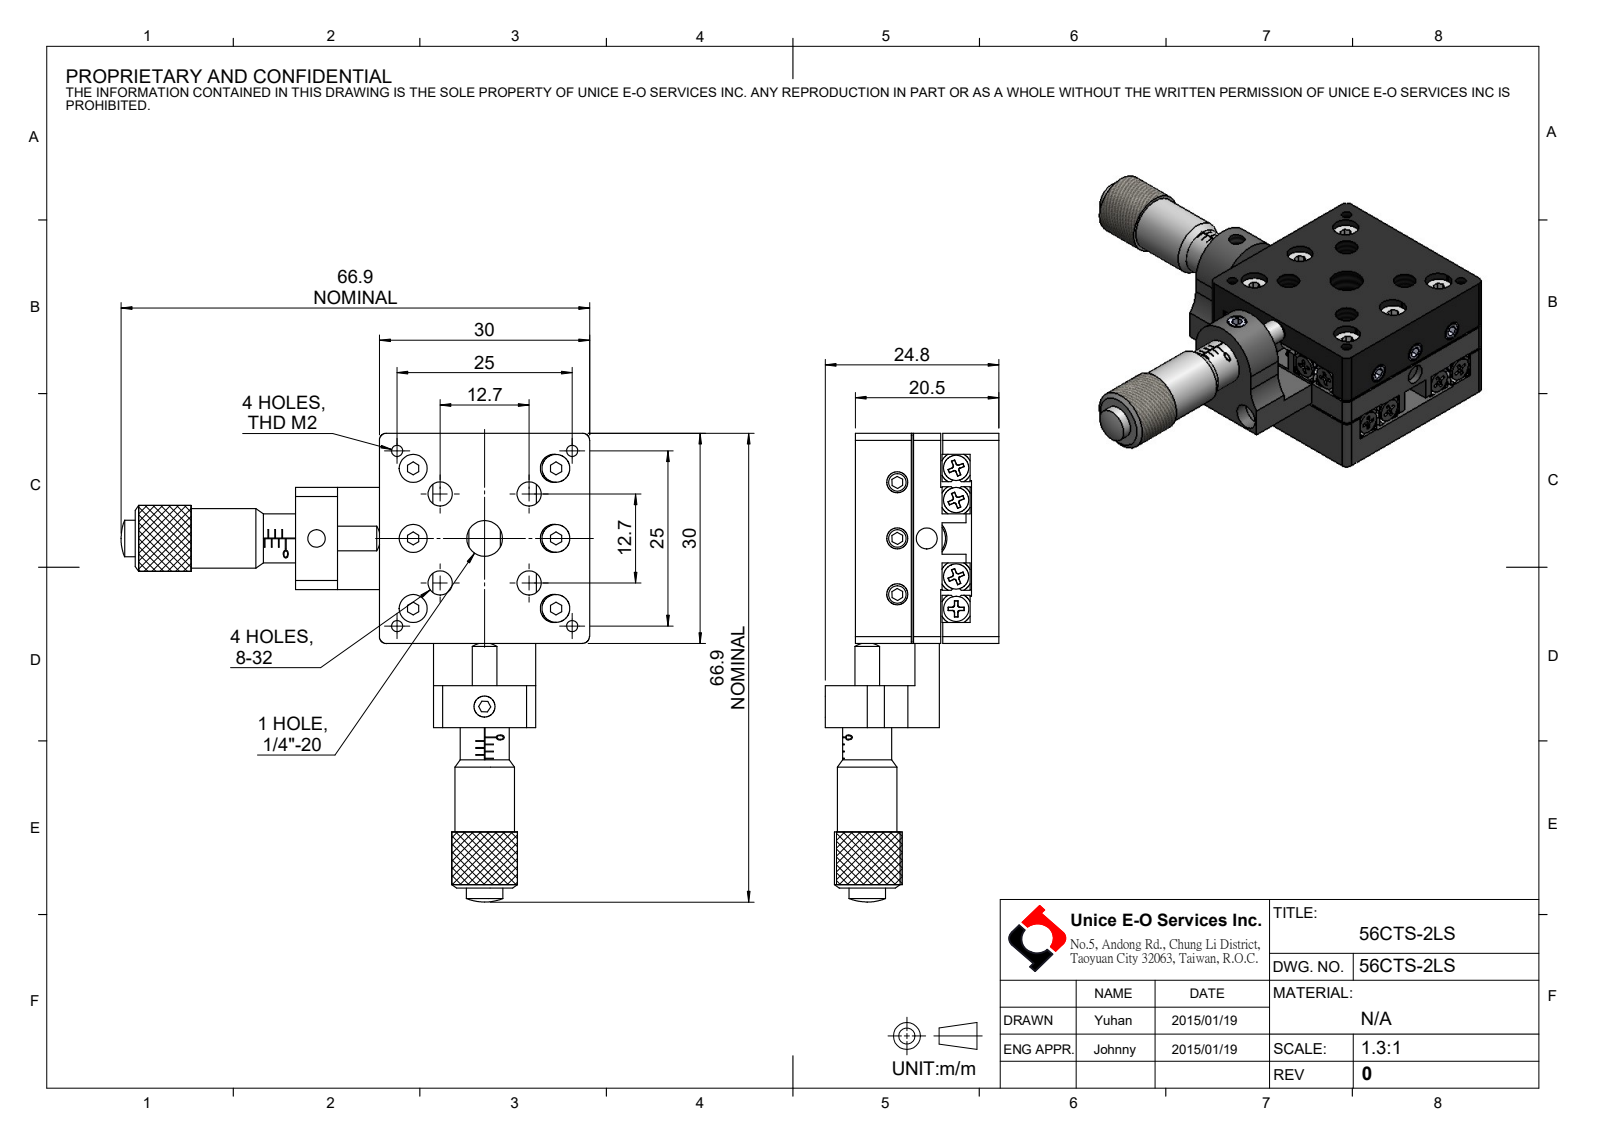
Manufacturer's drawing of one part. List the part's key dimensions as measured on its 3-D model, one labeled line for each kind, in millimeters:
Part name (STEP PRODUCT): 56CTS-2LS
STEP written by: SolidWorks 2016 (CONFIG_CONTROL_DESIGN)
Units: millimetres
Bodies: 61 solids, 1740 faces (971 planar, 497 cylindrical, 272 other)
Overall size (bounding box): 66.9 × 66.9 × 24.8
Volume: 20 374 mm³ · Surface area: 23 718 mm²
Round holes (diameter × count): ⌀1.6 ×44, ⌀4 ×22, ⌀2.4 ×12, ⌀2.5 ×11, ⌀2.1 ×4, ⌀3.45 ×4, ⌀2.6 ×3, ⌀4.2 ×3, ⌀3 ×2, ⌀3.5 ×2, ⌀6 ×2, ⌀5.11 ×1
Round bosses / shafts (diameter × count): ⌀2 ×18, ⌀4 ×8, ⌀3.6 ×8, ⌀3 ×8, ⌀1.95 ×8, ⌀9.4 ×2, ⌀8.5 ×2, ⌀7 ×2
Partial cylindrical surfaces — rounded edges, fillets, slot ends (radius × count): R1.25 ×11, R2 ×5, R1 ×4, R5 ×4, R6 ×2
Main face-to-face distances: 8.3, 8.1, 3.9, 4.1, 4.2, 8.5, 4, 12.4, 4.4, 12.5
Hole centre spacings: 10, 11.14, 15.5, 4.9, 18.45, 19.83, 5.3, 10.2
